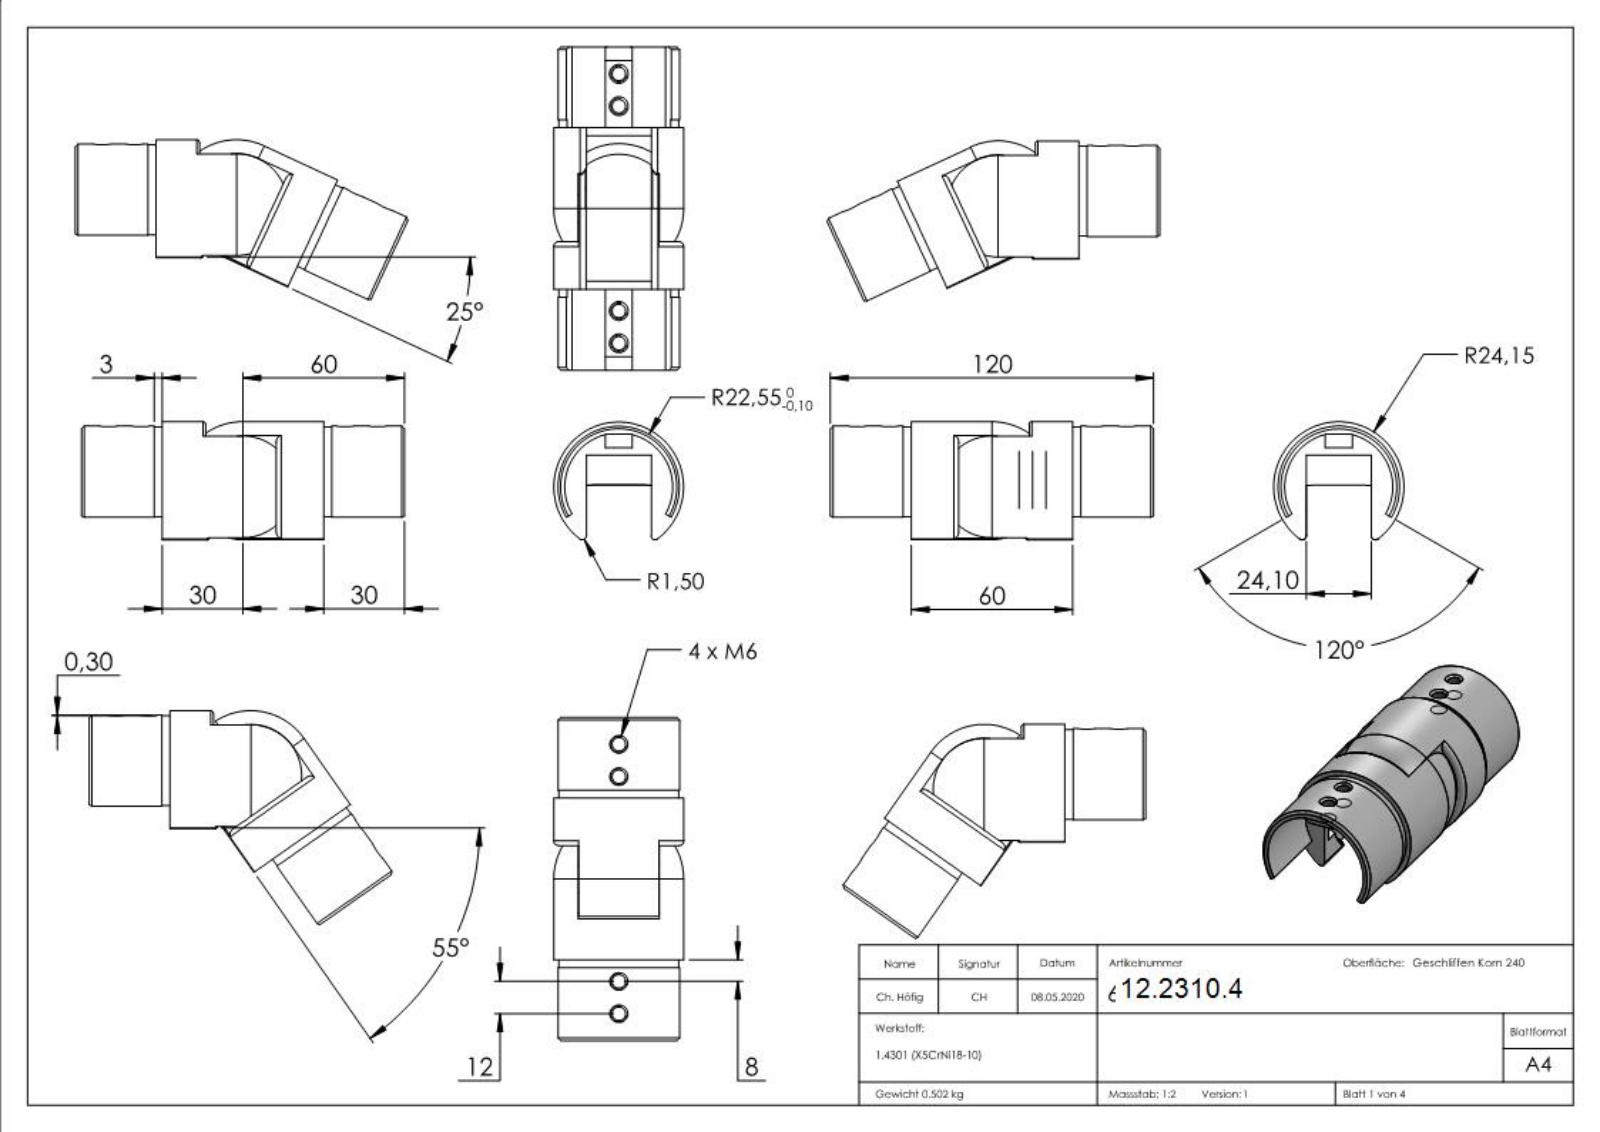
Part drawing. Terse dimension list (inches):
name: 60315-240; 60315-240 Teil1_60315-240 Teil1; 60315-240 Teil2_60313-240 Teil1
written by: SolidWorks 2015 (CONFIG_CONTROL_DESIGN)
unit: in
bodies: 2 solids, 313 faces (154 planar, 24 cylindrical, 135 other)
size: 4.724 × 1.902 × 1.724
volume: 3.834 in³; area: 53.11 in²
holes: 4× ⌀0.197, 1× ⌀0.398
bosses: 1× ⌀1.902, 1× ⌀0.394
rounds: 4× R0.059, 1× R0.789, 1× R0.793, 1× R0.876, 1× R0.888
face distances: 0.116, 1.069, 1.063, 1.179, 0.11, 0.953, 1.185, 1.173, 0.118, 2.362
hole spacings: 0.472, 3.465, 2.992, 3.937
